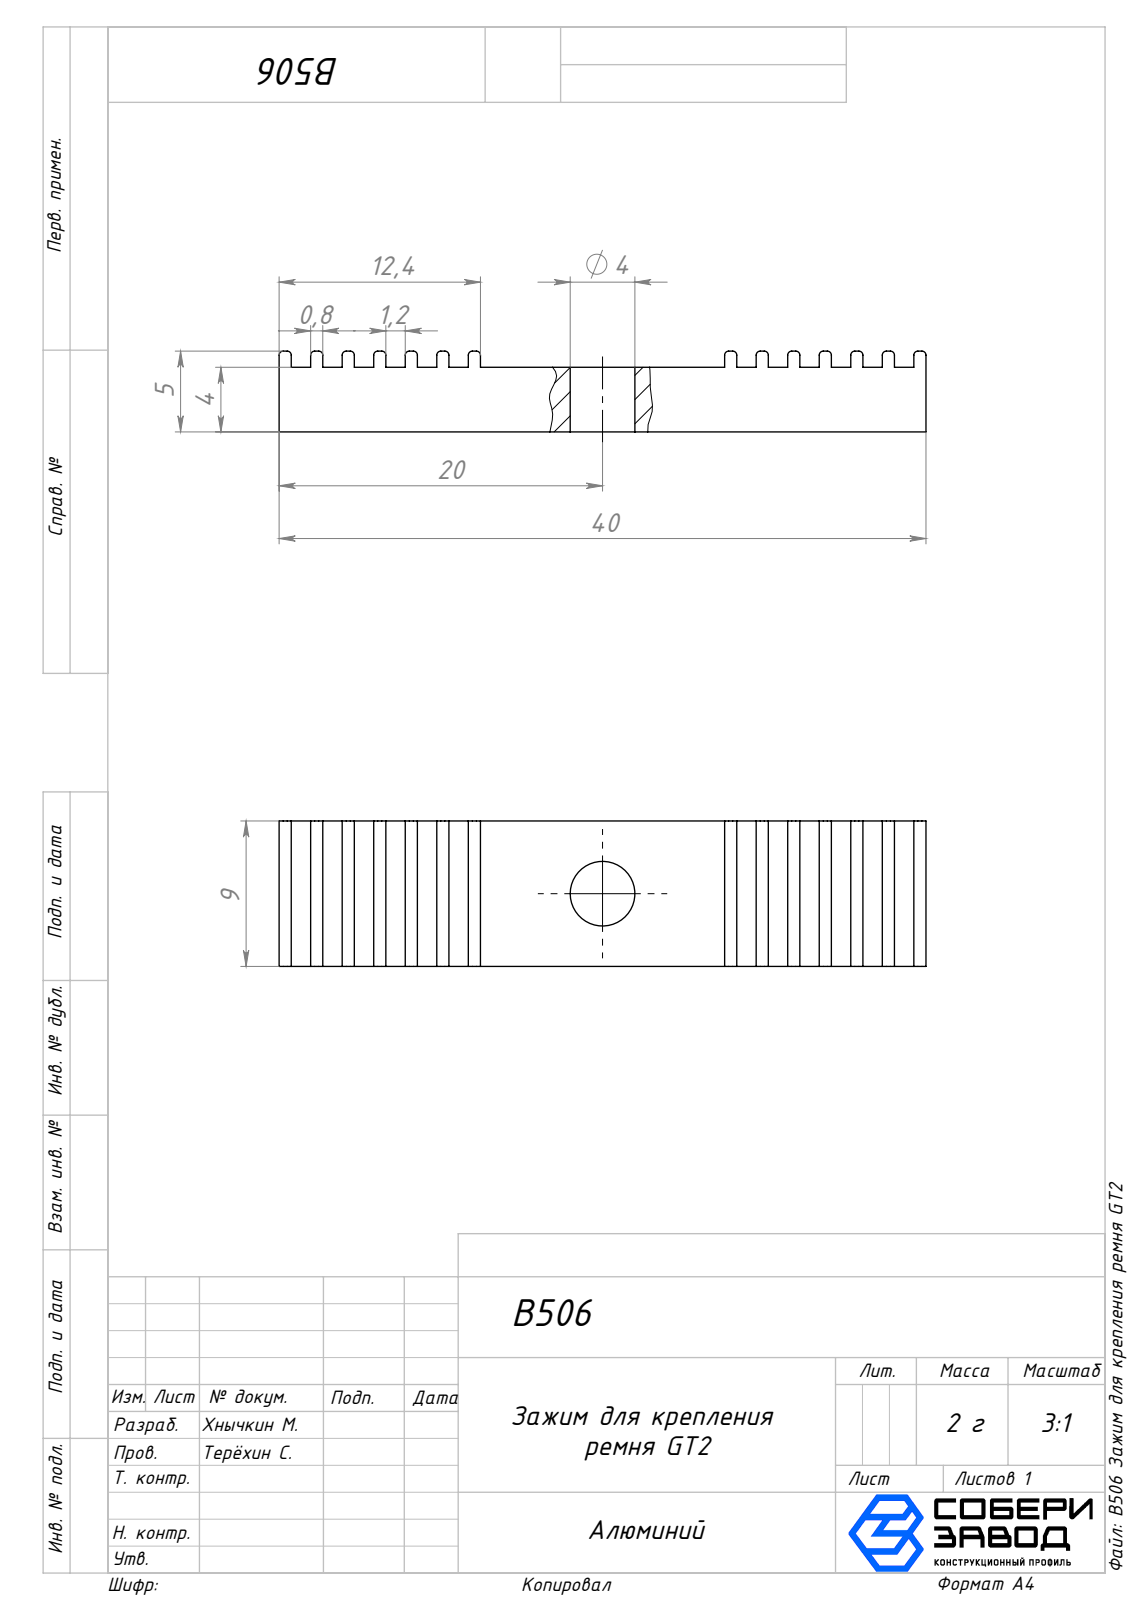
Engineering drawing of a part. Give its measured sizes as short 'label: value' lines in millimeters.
name: B506 Зажим для крепления ремня GT2
written by: SolidWorks 2025 (AUTOMOTIVE_DESIGN)
unit: mm
bodies: 1 solid, 88 faces (58 planar, 30 cylindrical, 0 other)
size: 40 × 9 × 5
volume: 1 481 mm³; area: 1 382 mm²
holes: 1× ⌀4
rounds: 28× R0.25
face distances: 4, 9, 1.95, 3.9, 0.75, 2.7, 5.85, 1.2, 40, 4.65
